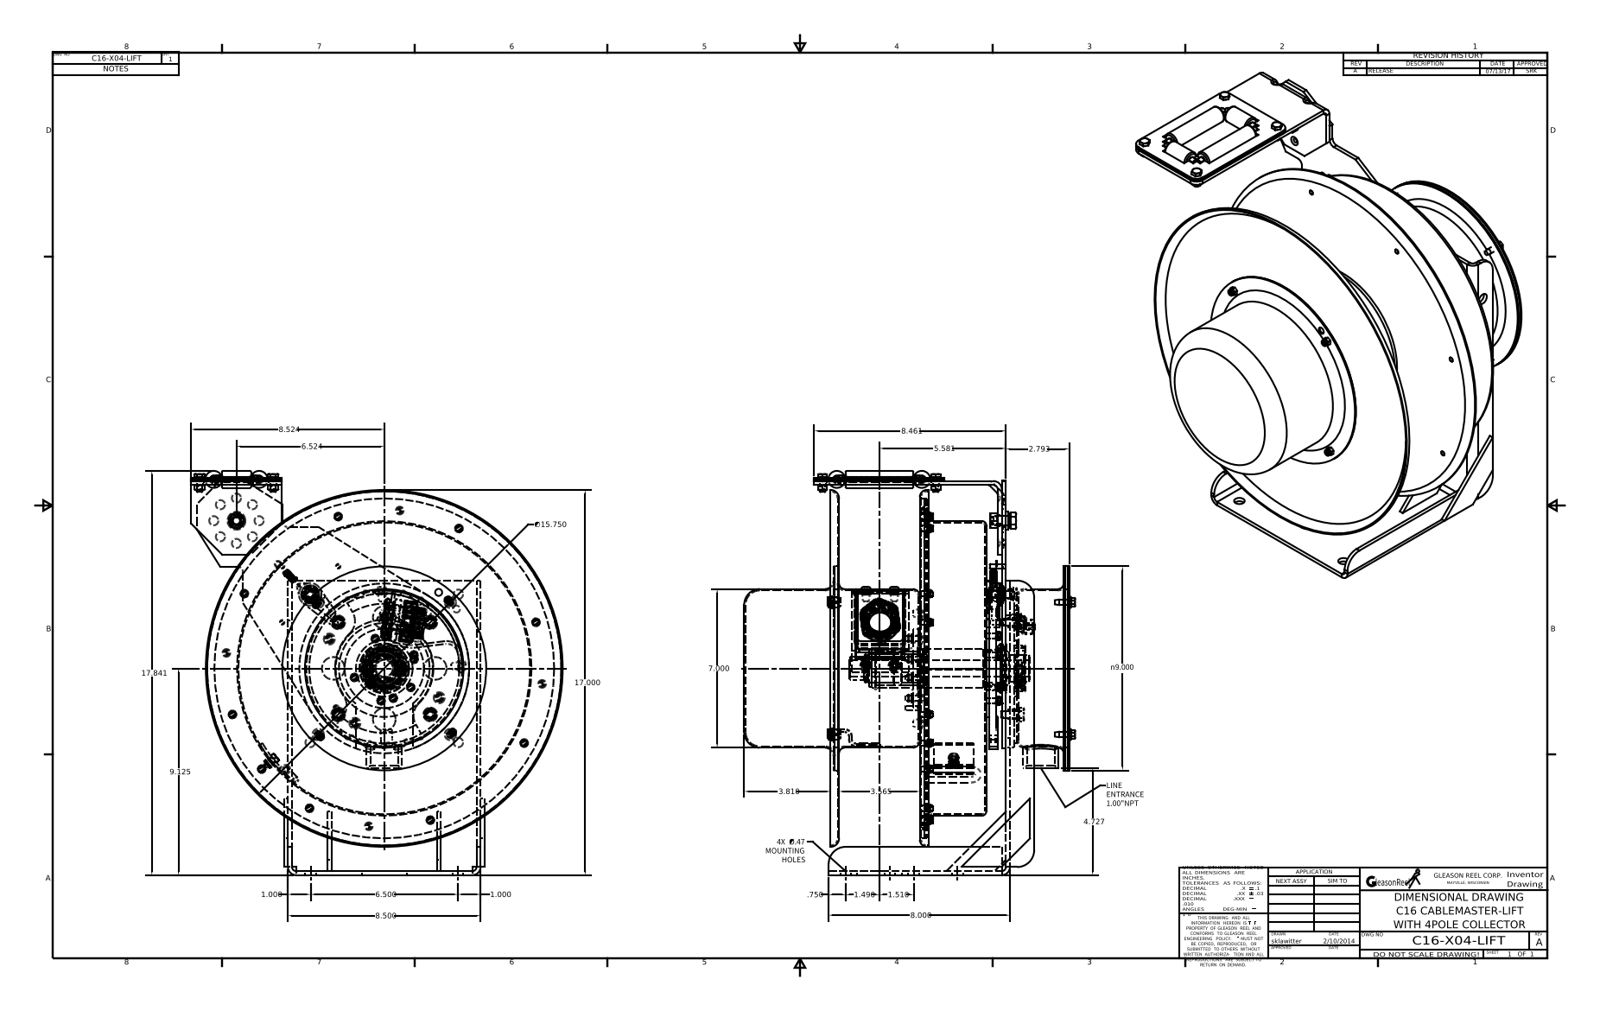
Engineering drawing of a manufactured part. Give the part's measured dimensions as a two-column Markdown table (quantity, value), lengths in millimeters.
| quantity | value |
| --- | --- |
| part name | C16-X04-LIFT (SW) |
| STEP written by | Autodesk Inventor 2016 (AUTOMOTIVE_DESIGN) |
| units | millimeters |
| bodies | 158 solids, 3254 faces (1277 planar, 1020 cylindrical, 957 other) |
| overall size | 453.16 × 416.53 × 370.97 |
| volume | 3 110 000 mm³ |
| surface area | 2 568 000 mm² |
| round holes (diameter × count) | 6.35 × 28, 5 × 26, 4.13 × 22, 10.31 × 13, 5.56 × 12, 5.41 × 8, 10.67 × 8, 11.94 × 8, 7.14 × 7, 4.92 × 5, 25.4 × 5, 2.32 × 4 |
| round bosses / shafts (diameter × count) | 5 × 26, 6.8 × 13, 6 × 10, 12.7 × 5, 11.6 × 5, 8.9 × 5, 8 × 5, 19.05 × 4 |
| partial cylindrical surfaces (radius × count) | 0.76 × 67, 0.24 × 64, 0.38 × 58, 1.98 × 18, 0.15 × 12, 1.52 × 12, 3.15 × 8, 6.35 × 8 |
| main face-to-face distances | 1.52, 4.55, 3.17, 165.02, 4.7, 96.75, 98.28, 1.53, 1.5, 6.2 |
| hole center spacings | 103.2, 44.43, 103.25, 145.95, 190.49, 44.54, 46.93, 49.28 |
